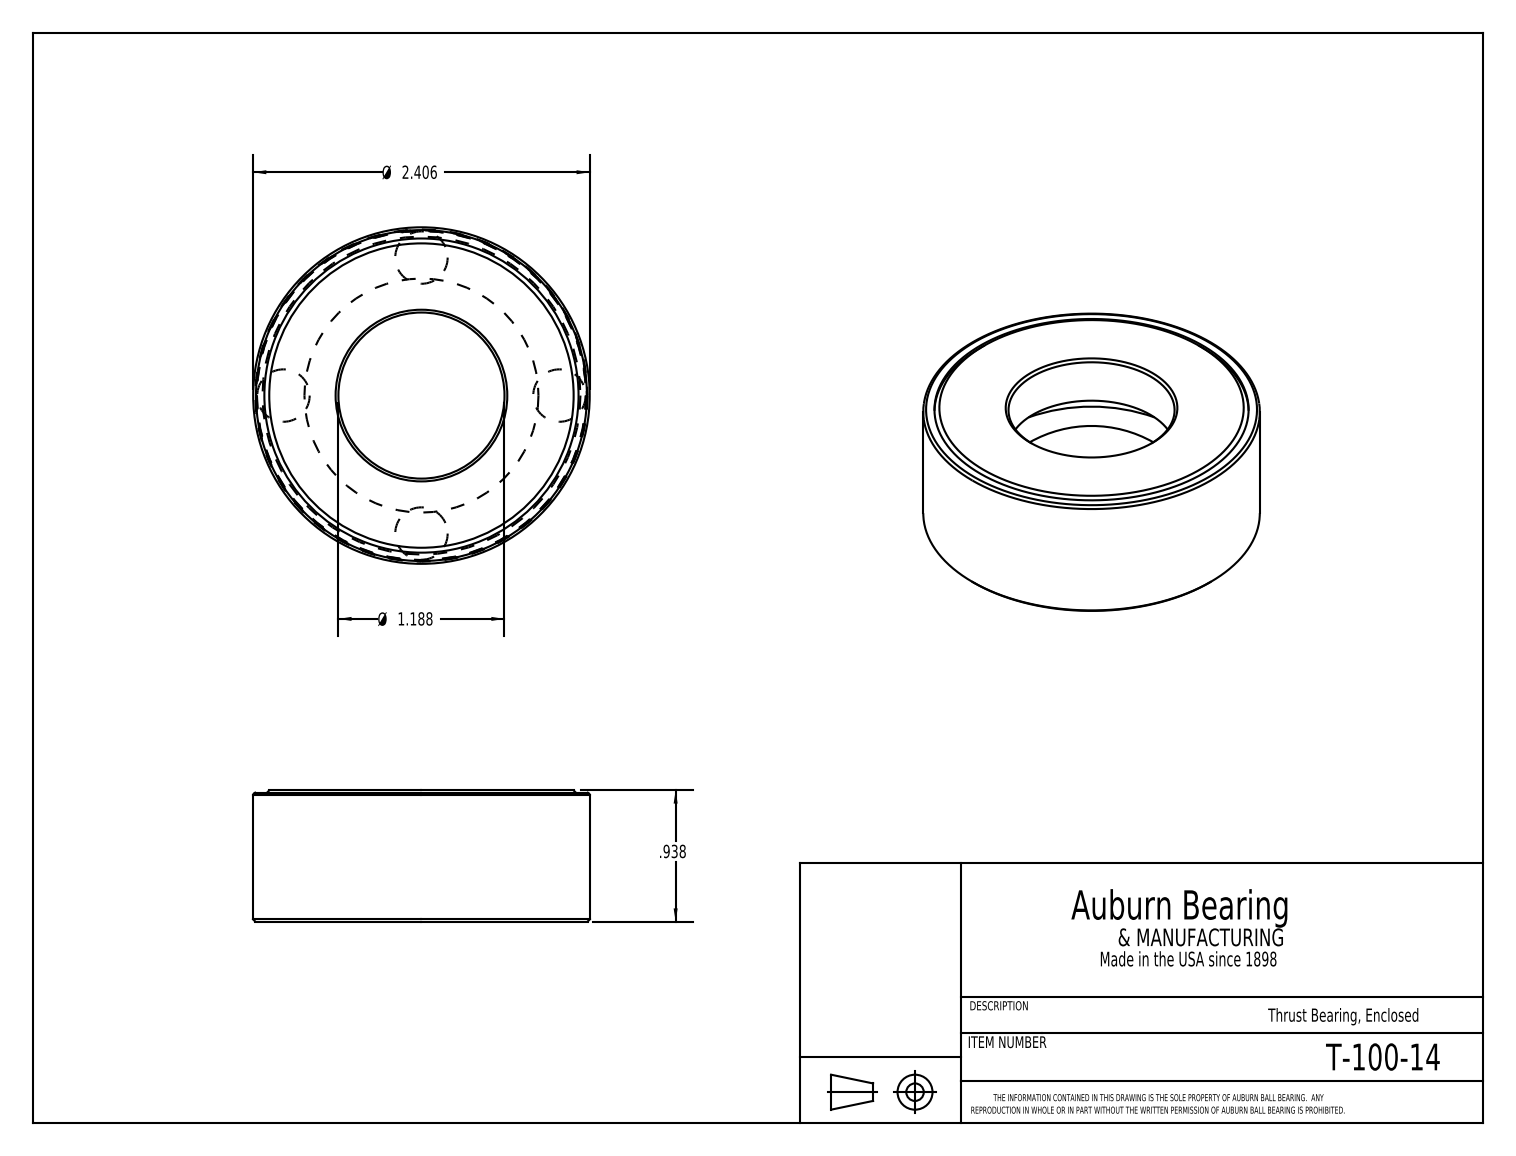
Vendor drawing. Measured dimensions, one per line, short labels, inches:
name: T-100-14
written by: SolidWorks 2016 (CONFIG_CONTROL_DESIGN)
unit: in
bodies: 6 solids, 28 faces (9 planar, 7 cylindrical, 12 other)
size: 2.406 × 2.406 × 0.938
volume: 2.357 in³; area: 32.49 in²
holes: 1× ⌀1.187, 1× ⌀2.246, 1× ⌀2.366
bosses: 1× ⌀2.406, 1× ⌀2.352
face distances: 0.356, 0.581, 0.937, 0.225, 0.902, 0.922, 0.546, 0.566, 0.321, 0.341
